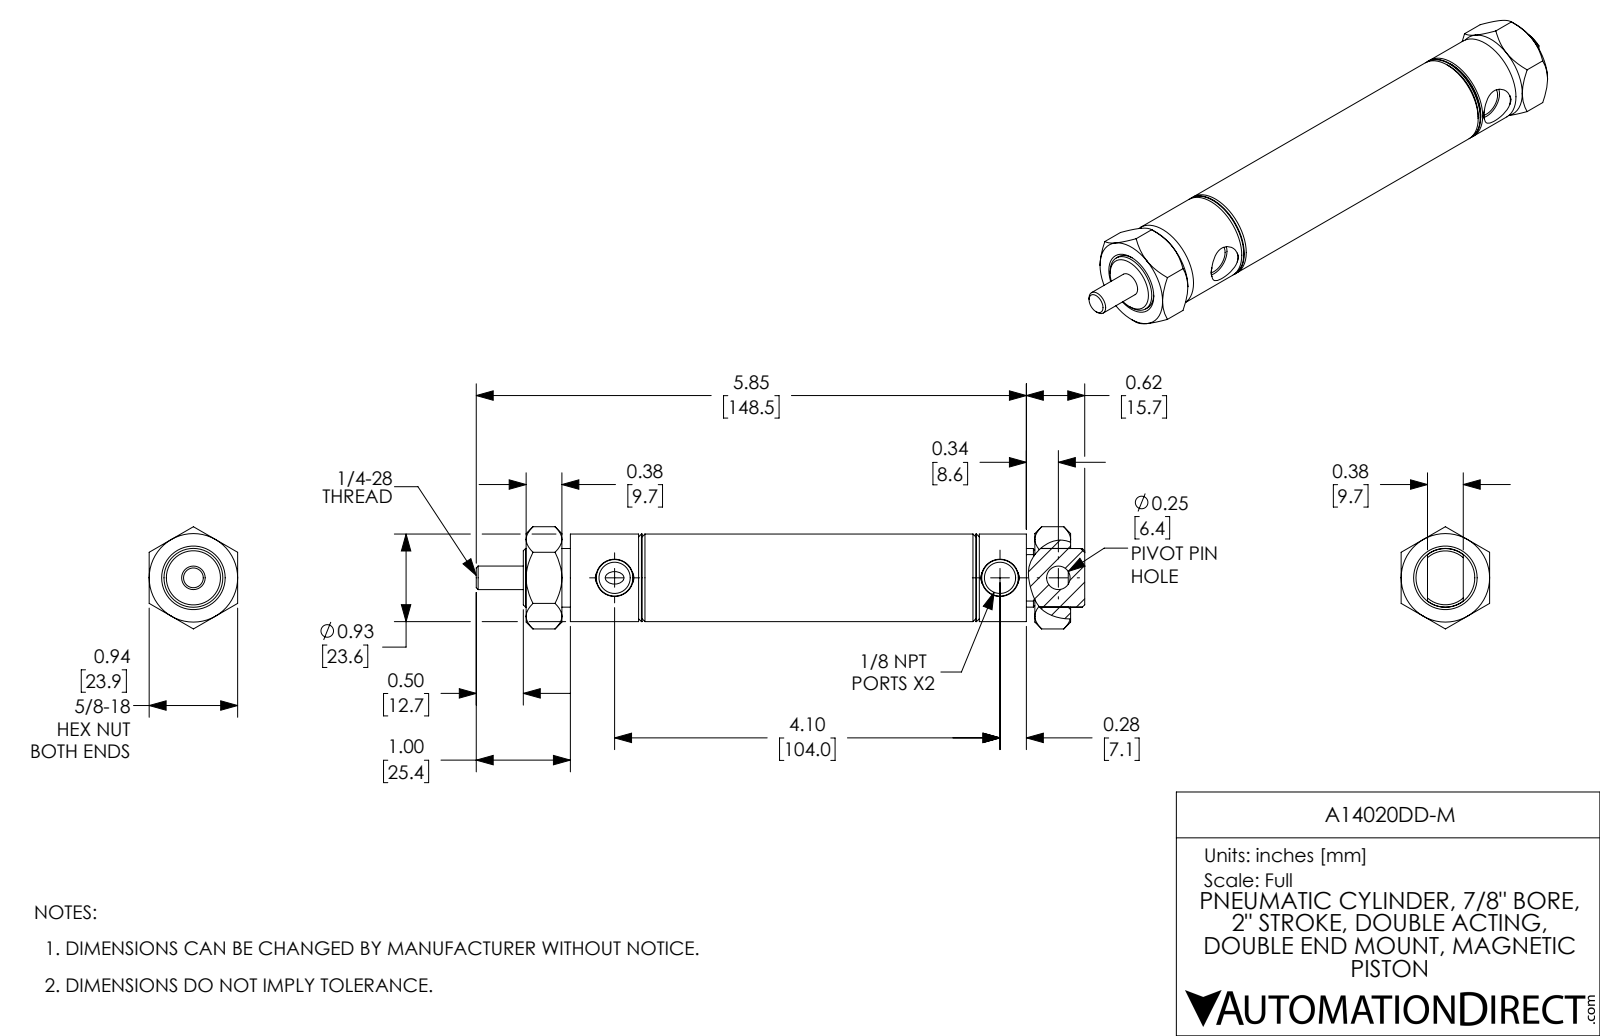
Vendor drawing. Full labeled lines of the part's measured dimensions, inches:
Part name (STEP PRODUCT): A14020DD-M; A14020DD-M_Mounting Nut_D-9; A14020DD-M-Rod; A14020DD-M-MainBody
STEP written by: SolidWorks 2017 (AUTOMOTIVE_DESIGN)
Units: inches
Bodies: 4 solids, 137 faces (35 planar, 38 cylindrical, 64 other)
Overall size (bounding box): 6.465 × 1.085 × 0.94
Volume: 2.747 in³ · Surface area: 39.75 in²
Round holes (diameter × count): ⌀0.25 ×2, ⌀0.332 ×2, ⌀0.625 ×1, ⌀0.875 ×1
Round bosses / shafts (diameter × count): ⌀0.93 ×1, ⌀0.623 ×1, ⌀0.562 ×1
Main face-to-face distances: 0.94, 0.5, 4.935, 0.09, 0.47, 5.315, 5.405, 0.38, 3.785, 2.5
Hole centre spacings: 0.62, 4.095, 4.715
